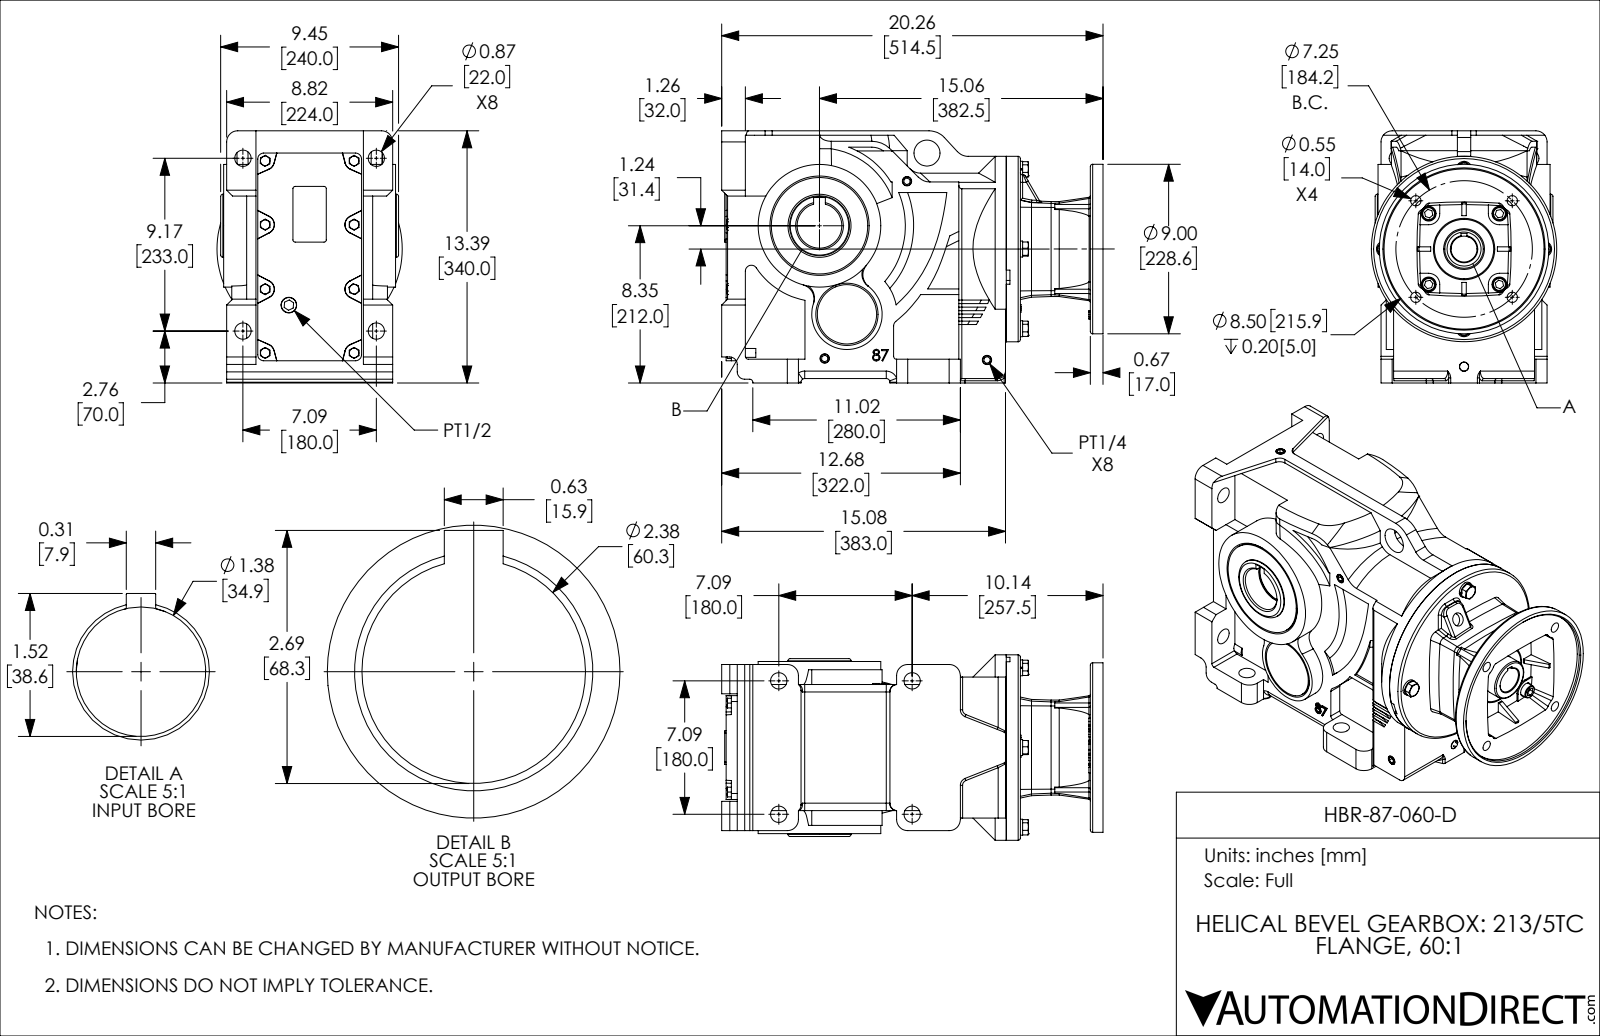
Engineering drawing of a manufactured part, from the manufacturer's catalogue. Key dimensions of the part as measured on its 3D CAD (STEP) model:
Part name (STEP PRODUCT): HBR-87-060-D
STEP written by: SolidWorks 2018 (AUTOMOTIVE_DESIGN)
Units: inches
Bodies: 9 solids, 1185 faces (575 planar, 309 cylindrical, 301 other)
Overall size (bounding box): 20.256 × 13.501 × 9.843
Volume: 1 441 in³ · Surface area: 1 528 in²
Round holes (diameter × count): ⌀0.551 ×8, ⌀0.866 ×8, ⌀0.48 ×4, ⌀0.496 ×4, ⌀0.787 ×4, ⌀0.473 ×1, ⌀0.709 ×1, ⌀0.827 ×1, ⌀1.125 ×1, ⌀1.376 ×1, ⌀1.378 ×1, ⌀1.417 ×1
Round bosses / shafts (diameter × count): ⌀0.846 ×4, ⌀0.709 ×4, ⌀0.472 ×4, ⌀3.15 ×2, ⌀9.843 ×1, ⌀9 ×1, ⌀6.513 ×1, ⌀5.118 ×1
Partial cylindrical surfaces — rounded edges, fillets, slot ends (radius × count): R0.591 ×22, R0.394 ×17, R0.118 ×15, R0.157 ×7, R0.315 ×6, R0.008 ×4, R0.236 ×4, R0.472 ×4
Main face-to-face distances: 0.669, 0.236, 6.024, 1.063, 7.087, 13.15, 0.394, 14.882, 1.22, 1.89
Hole centre spacings: 3.011, 6.394, 4.495, 7.087, 7.263, 2.657, 3.059, 3.758
